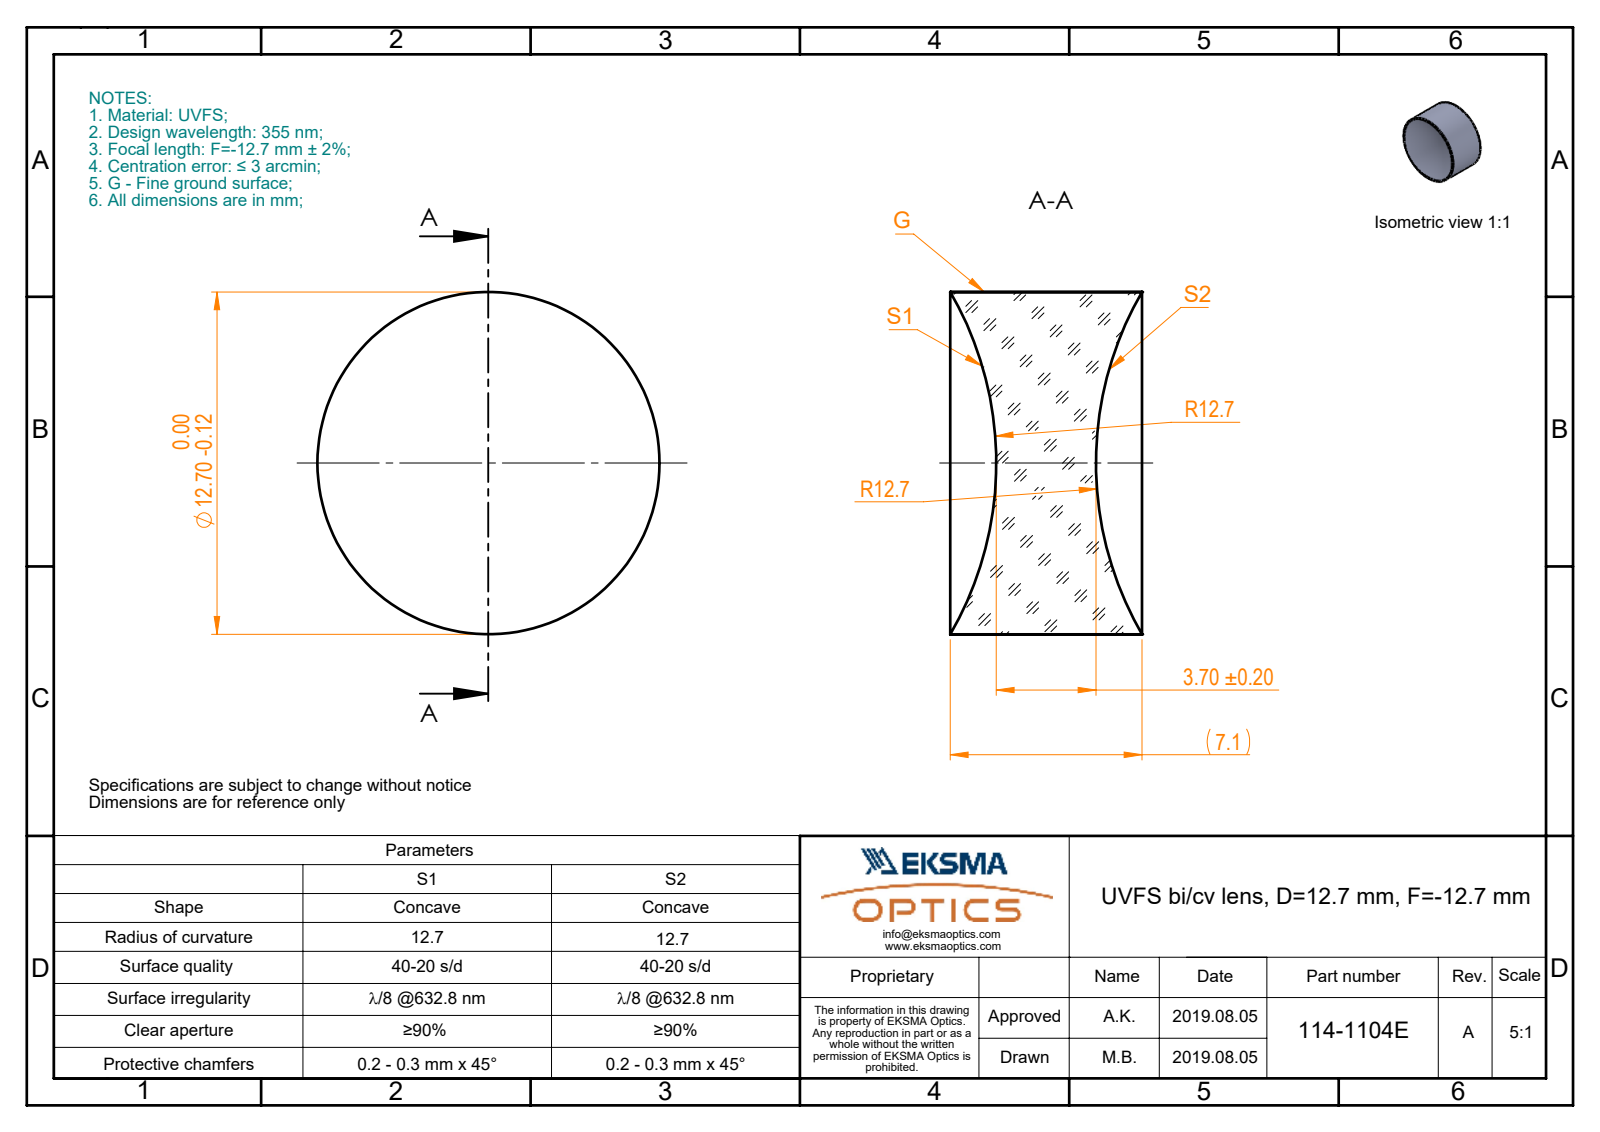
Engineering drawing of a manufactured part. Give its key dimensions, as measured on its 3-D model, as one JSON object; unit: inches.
{"part_name": "114-1104E UVFS bi-cv 12.7 F-12.7", "step_written_by": "SolidWorks 2017 (CONFIG_CONTROL_DESIGN)", "units": "inches", "bodies": {"solids": 1, "faces": 6, "planar": 0, "cylindrical": 2, "other": 4}, "overall_size": [0.5, 0.5, 0.28], "volume_in3": 0.041, "surface_area_in2": 0.862, "round_bosses_or_shafts": [[0.5, 1]]}
